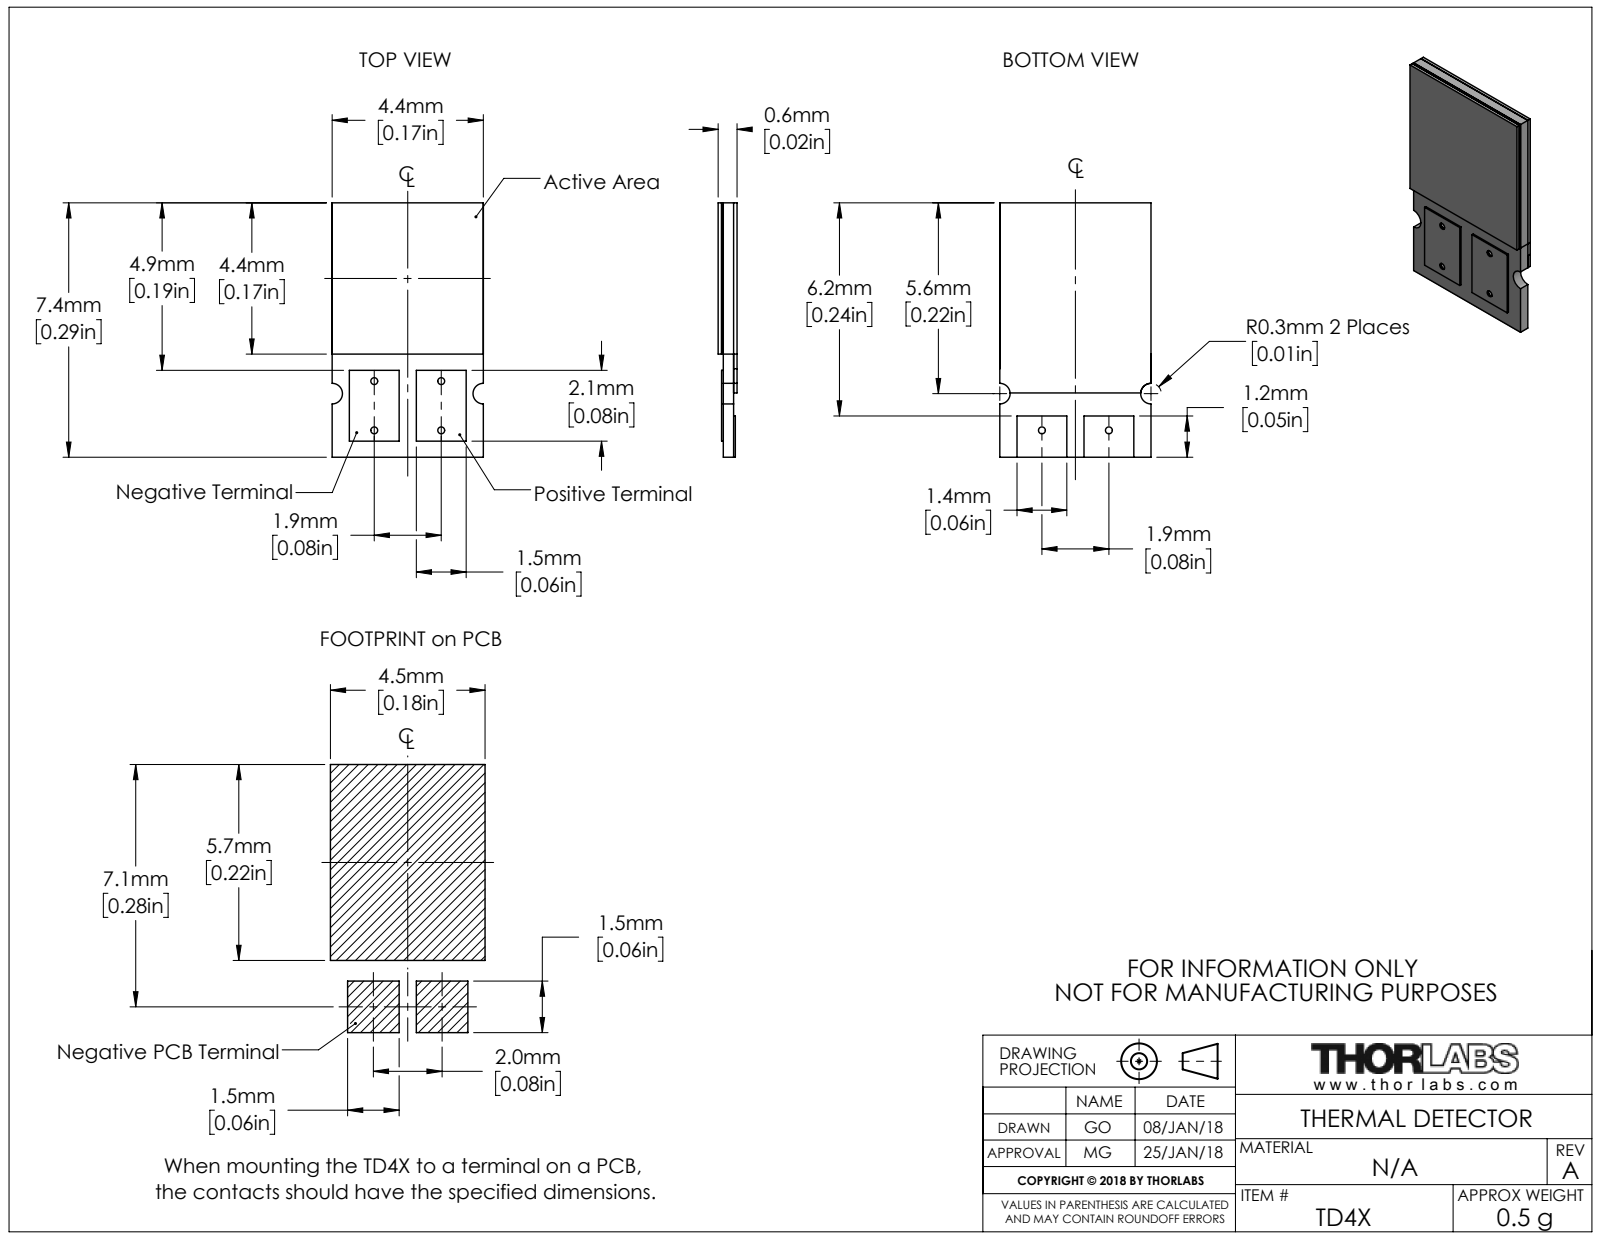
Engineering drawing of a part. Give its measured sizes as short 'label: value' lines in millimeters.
name: MTN10555-E0W
written by: SolidWorks 2016 (CONFIG_CONTROL_DESIGN)
unit: mm
bodies: 8 solids, 86 faces (57 planar, 29 cylindrical, 0 other)
size: 7.4 × 4.4 × 0.55
volume: 15 mm³; area: 223 mm²
holes: 4× ⌀0.2
rounds: 2× R0.3
face distances: 0.35, 0.45, 0.4, 0.55, 0.5, 4.4, 7.4, 3, 1.95, 1.87
hole spacings: 1.43, 1.94, 2.41
